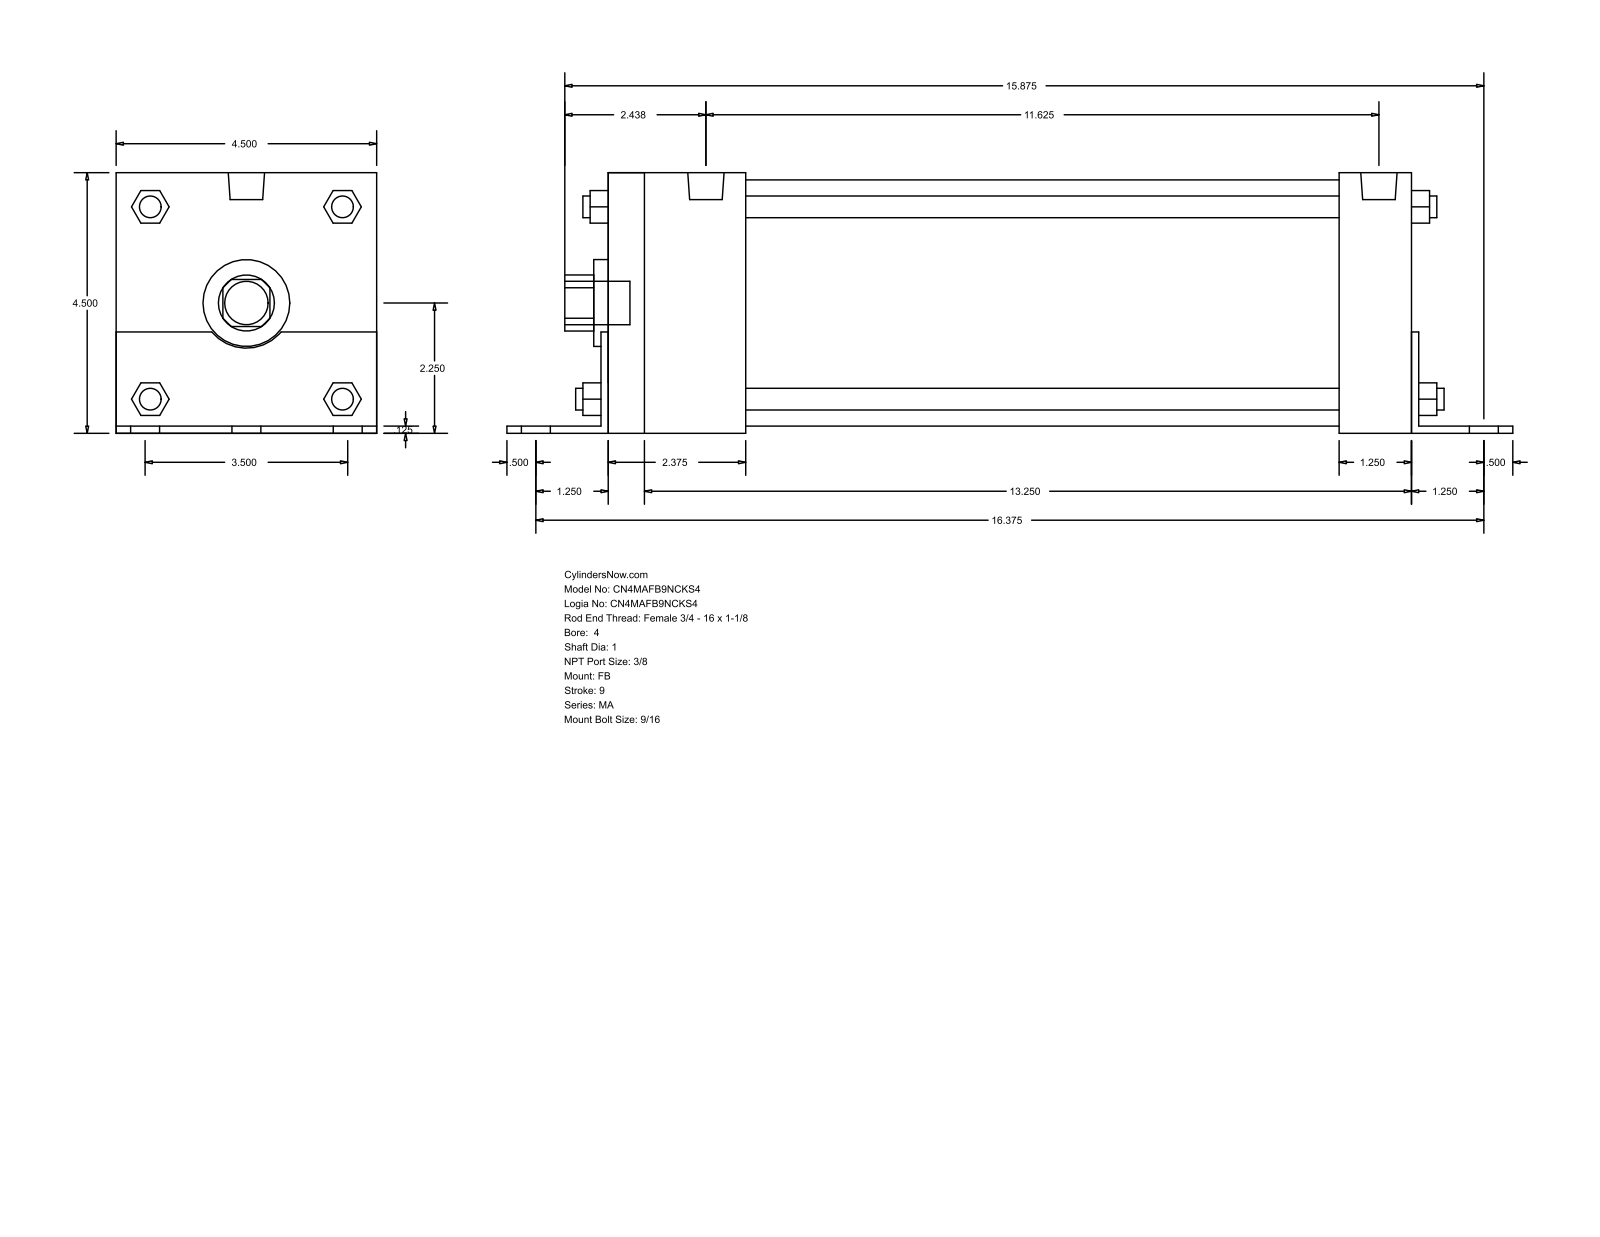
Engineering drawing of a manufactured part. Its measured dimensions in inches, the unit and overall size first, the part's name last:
Units: inches
Overall size (bounding box): 17.375 × 4.502 × 4.5
Round holes (diameter × count): ⌀1 ×1, ⌀1.5 ×1, ⌀4.25 ×1
Round bosses / shafts (diameter × count): ⌀0.563 ×6, ⌀0.437 ×4, ⌀0.375 ×4, ⌀0.627 ×2, ⌀0.75 ×1
Partial cylindrical surfaces — rounded edges, fillets, slot ends (radius × count): R0.484 ×1, R0.78 ×1
Main face-to-face distances: 4.5, 0.125, 4.502, 14, 0.123, 4.377, 13.875, 14.125, 12.75, 12.625
Bodies: 0 solids, 140 faces (105 planar, 35 cylindrical, 0 other)
Part name (STEP PRODUCT): MA_FB__0400_1
STEP written by: GSSL Pune (CONFIG_CONTROL_DESIGN)
